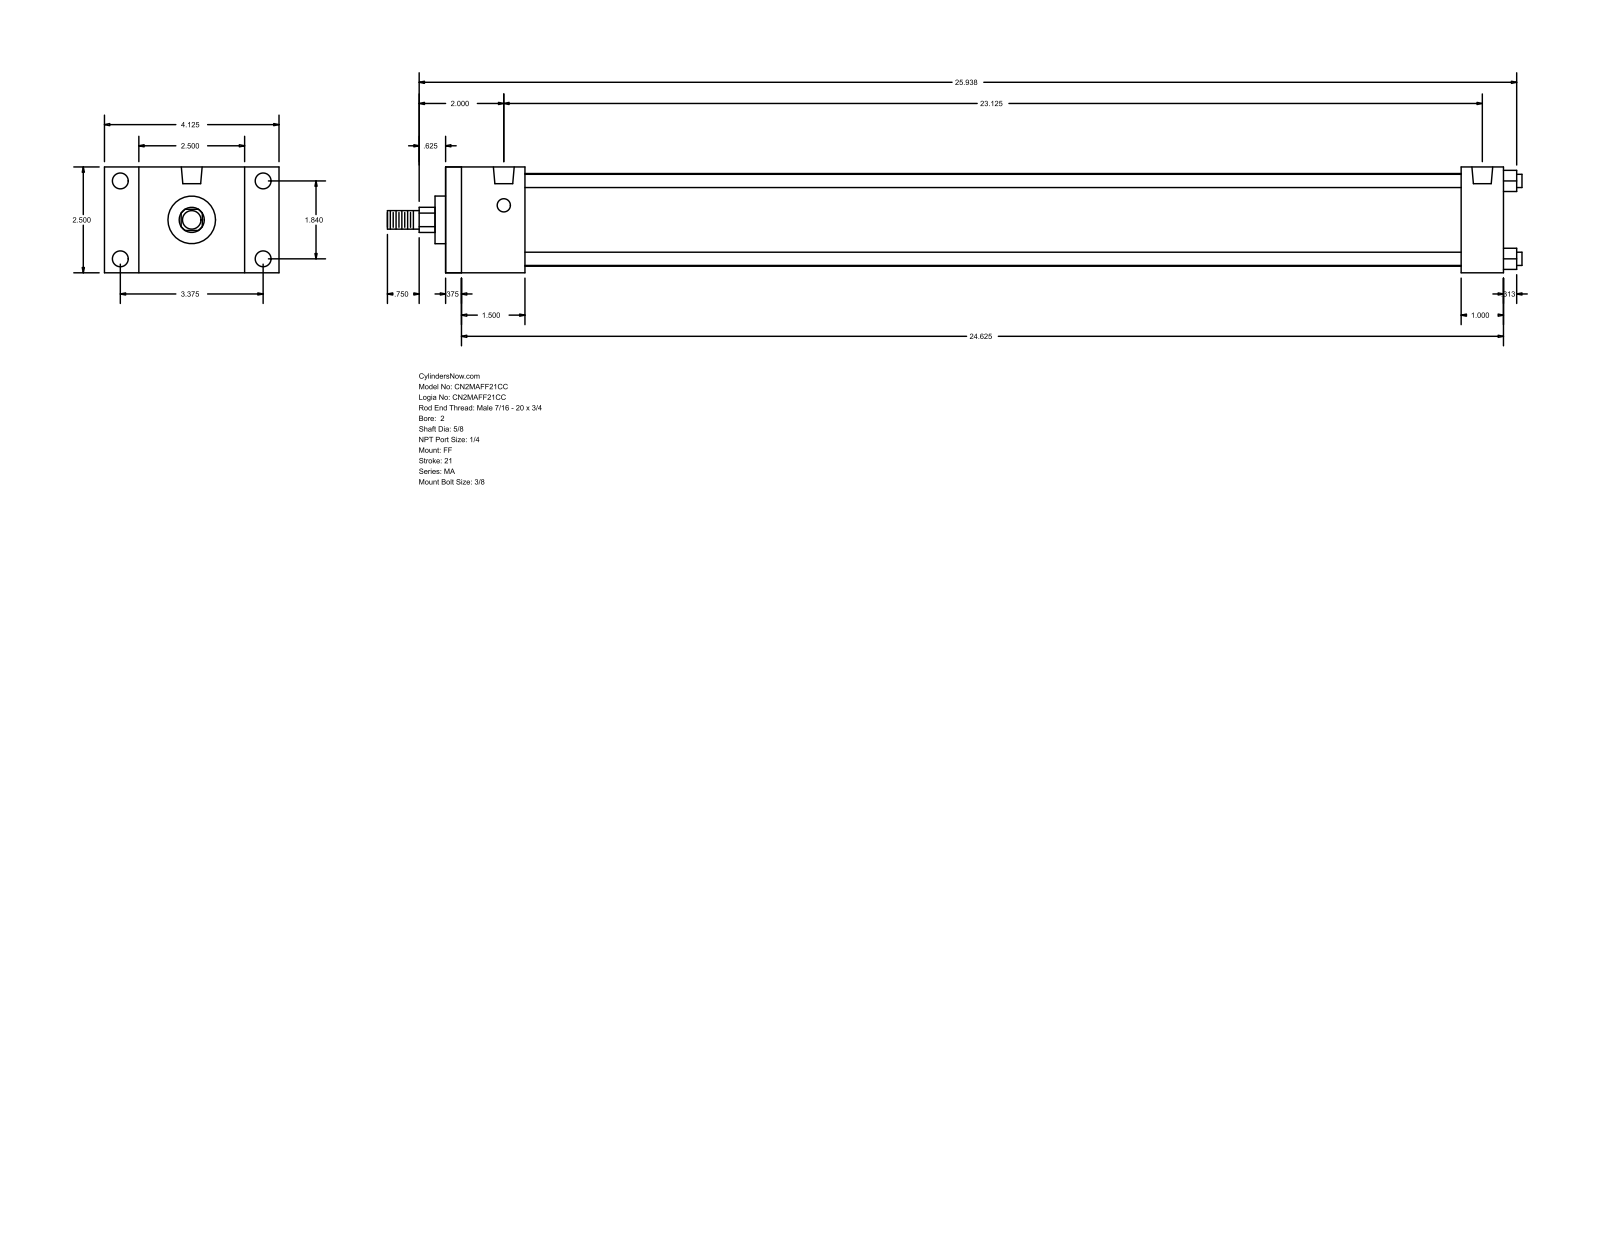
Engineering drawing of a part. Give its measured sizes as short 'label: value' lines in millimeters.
name: MA_FF__0200_0.625
written by: GSSL Pune (CONFIG_CONTROL_DESIGN)
unit: mm
bodies: 0 solids, 92 faces (64 planar, 28 cylindrical, 0 other)
size: 681.04 × 104.78 × 63.5
holes: 4× ⌀7.94, 4× ⌀9.53, 2× ⌀12.49
bosses: 4× ⌀7.94, 1× ⌀55.63, 1× ⌀28.57, 1× ⌀15.88, 1× ⌀11.11
rounds: 1× R7.54
face distances: 63.5, 635, 625.48, 9.52, 25.4, 38.1, 47.62, 609.6, 600.08, 561.98
hole spacings: 46.74, 85.72, 97.63, 587.37
